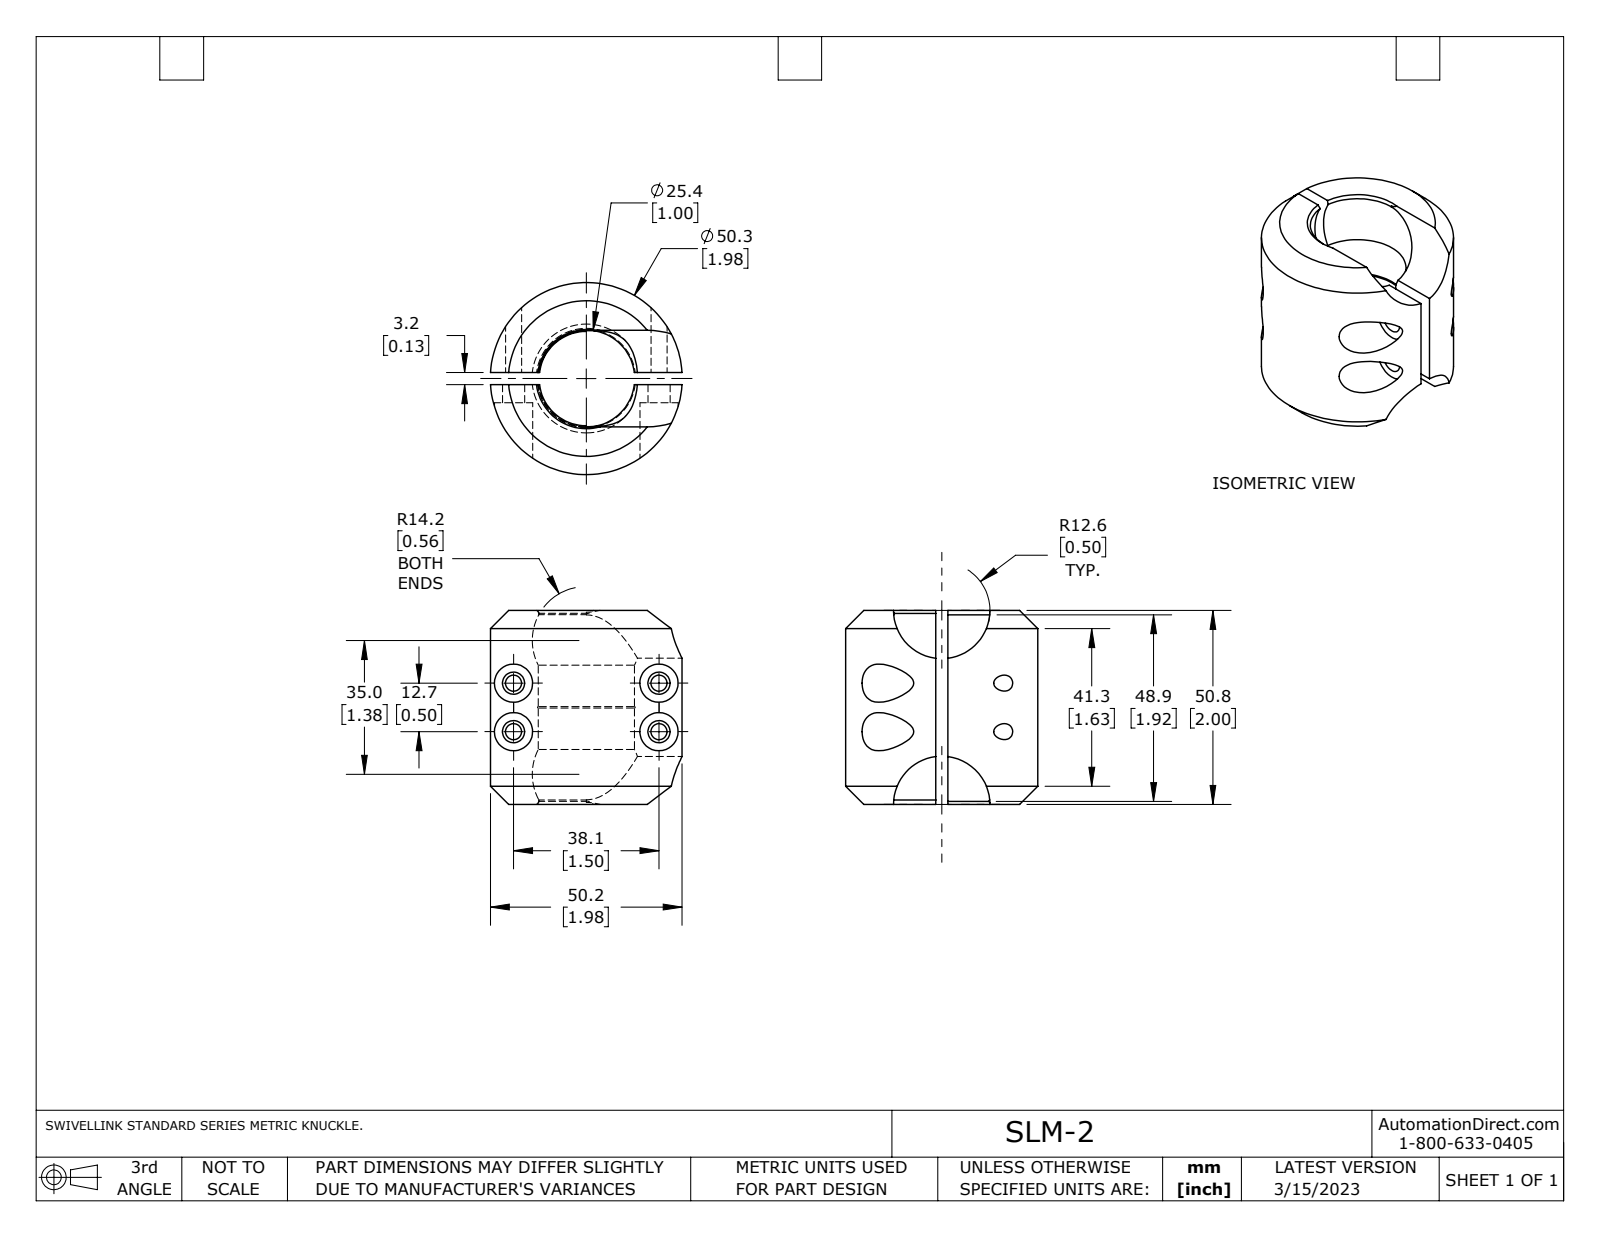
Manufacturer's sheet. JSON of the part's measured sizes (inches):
{"part_name": "SLM-2", "step_written_by": "SolidWorks 2021 (AUTOMOTIVE_DESIGN)", "units": "inches", "bodies": {"solids": 6, "faces": 124, "planar": 64, "cylindrical": 30, "other": 30}, "overall_size": [2, 1.98, 1.976], "volume_in3": 3.618, "surface_area_in2": 29.44, "round_holes": [[0.165, 4], [0.228, 4], [0.394, 4], [1, 1]], "round_bosses_or_shafts": [[0.339, 4], [0.198, 4], [1.98, 1]], "partial_cylinders_radius": [[0.497, 2]], "face_to_face_distances": [0.125, 2, 0.312, 0.187, 0.509, 0.384, 0.197, 0.148, 0.25, 0.361], "hole_center_spacings": [0.5, 1.5, 1.581]}
